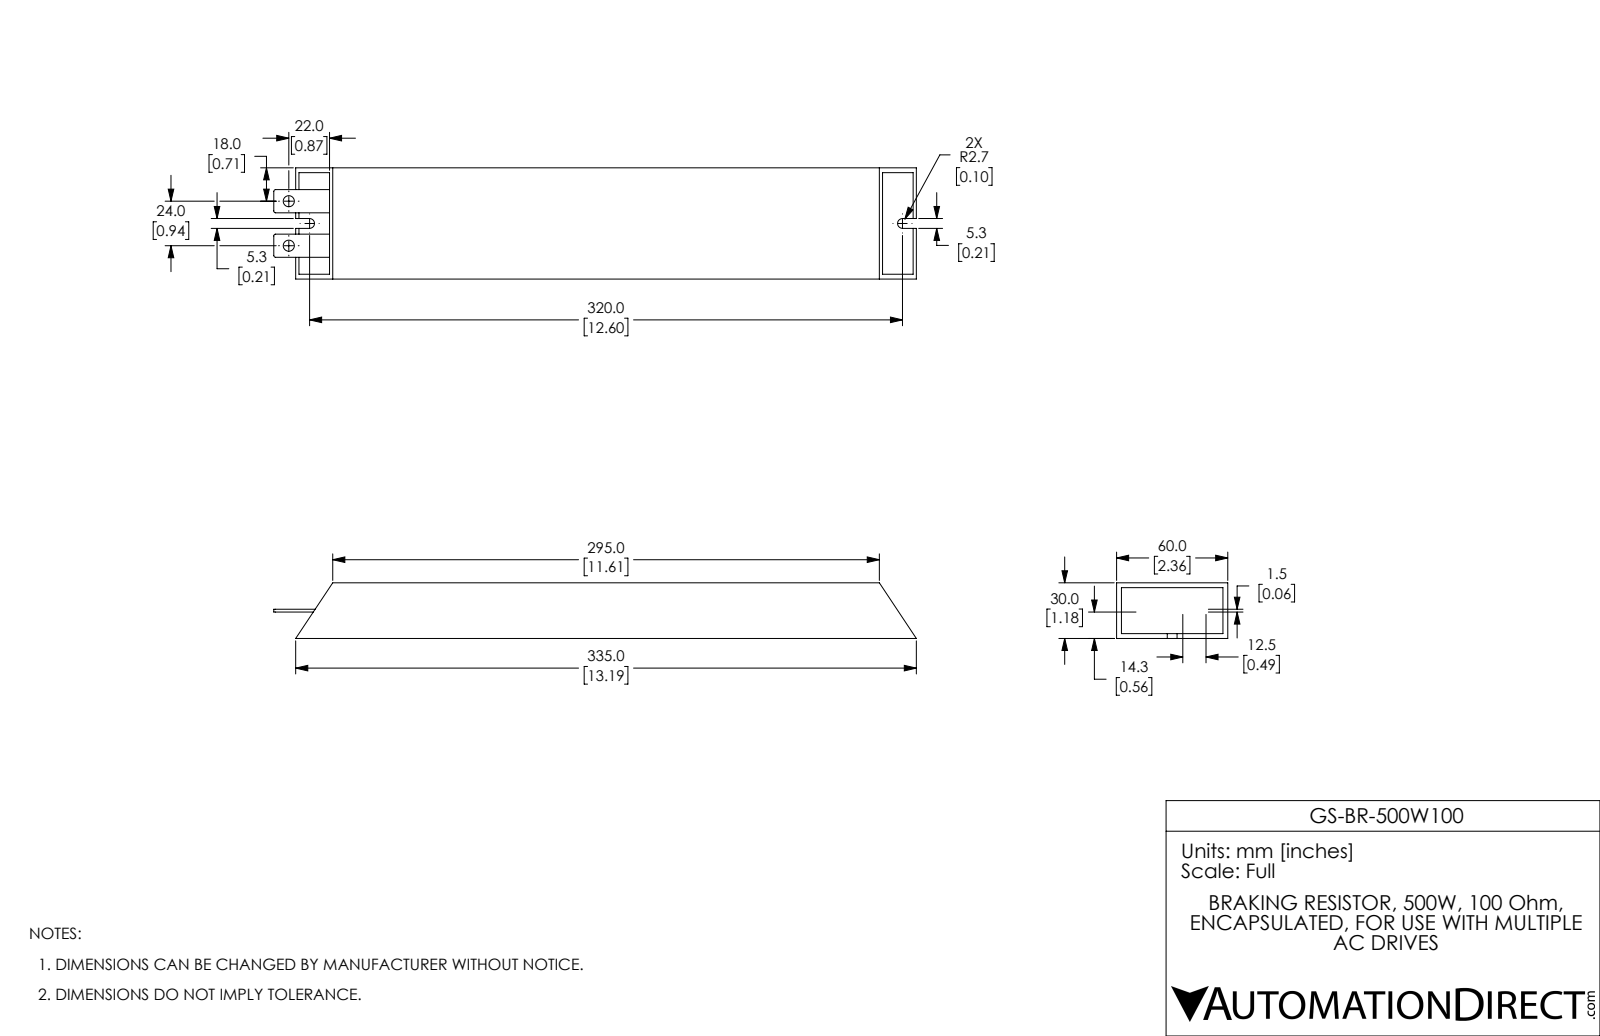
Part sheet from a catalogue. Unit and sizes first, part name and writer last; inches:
Units: inches
Overall size (bounding box): 13.655 × 2.362 × 1.181
Round holes (diameter × count): ⌀0.236 ×2
Partial cylindrical surfaces — rounded edges, fillets, slot ends (radius × count): R0.039 ×4, R0.104 ×2
Main face-to-face distances: 1.181, 2.362, 0.102, 1.079, 0.976, 2.26, 0.561, 0.62, 0.459, 0.518
Hole centre spacings: 0.945
Volume: 31.67 in³ · Surface area: 106.4 in²
Bodies: 3 solids, 42 faces (32 planar, 10 cylindrical, 0 other)
Part name (STEP PRODUCT): VFD-BR-A6-PD-3D00-BR500W100
STEP written by: SolidWorks 2017 (AUTOMOTIVE_DESIGN)
